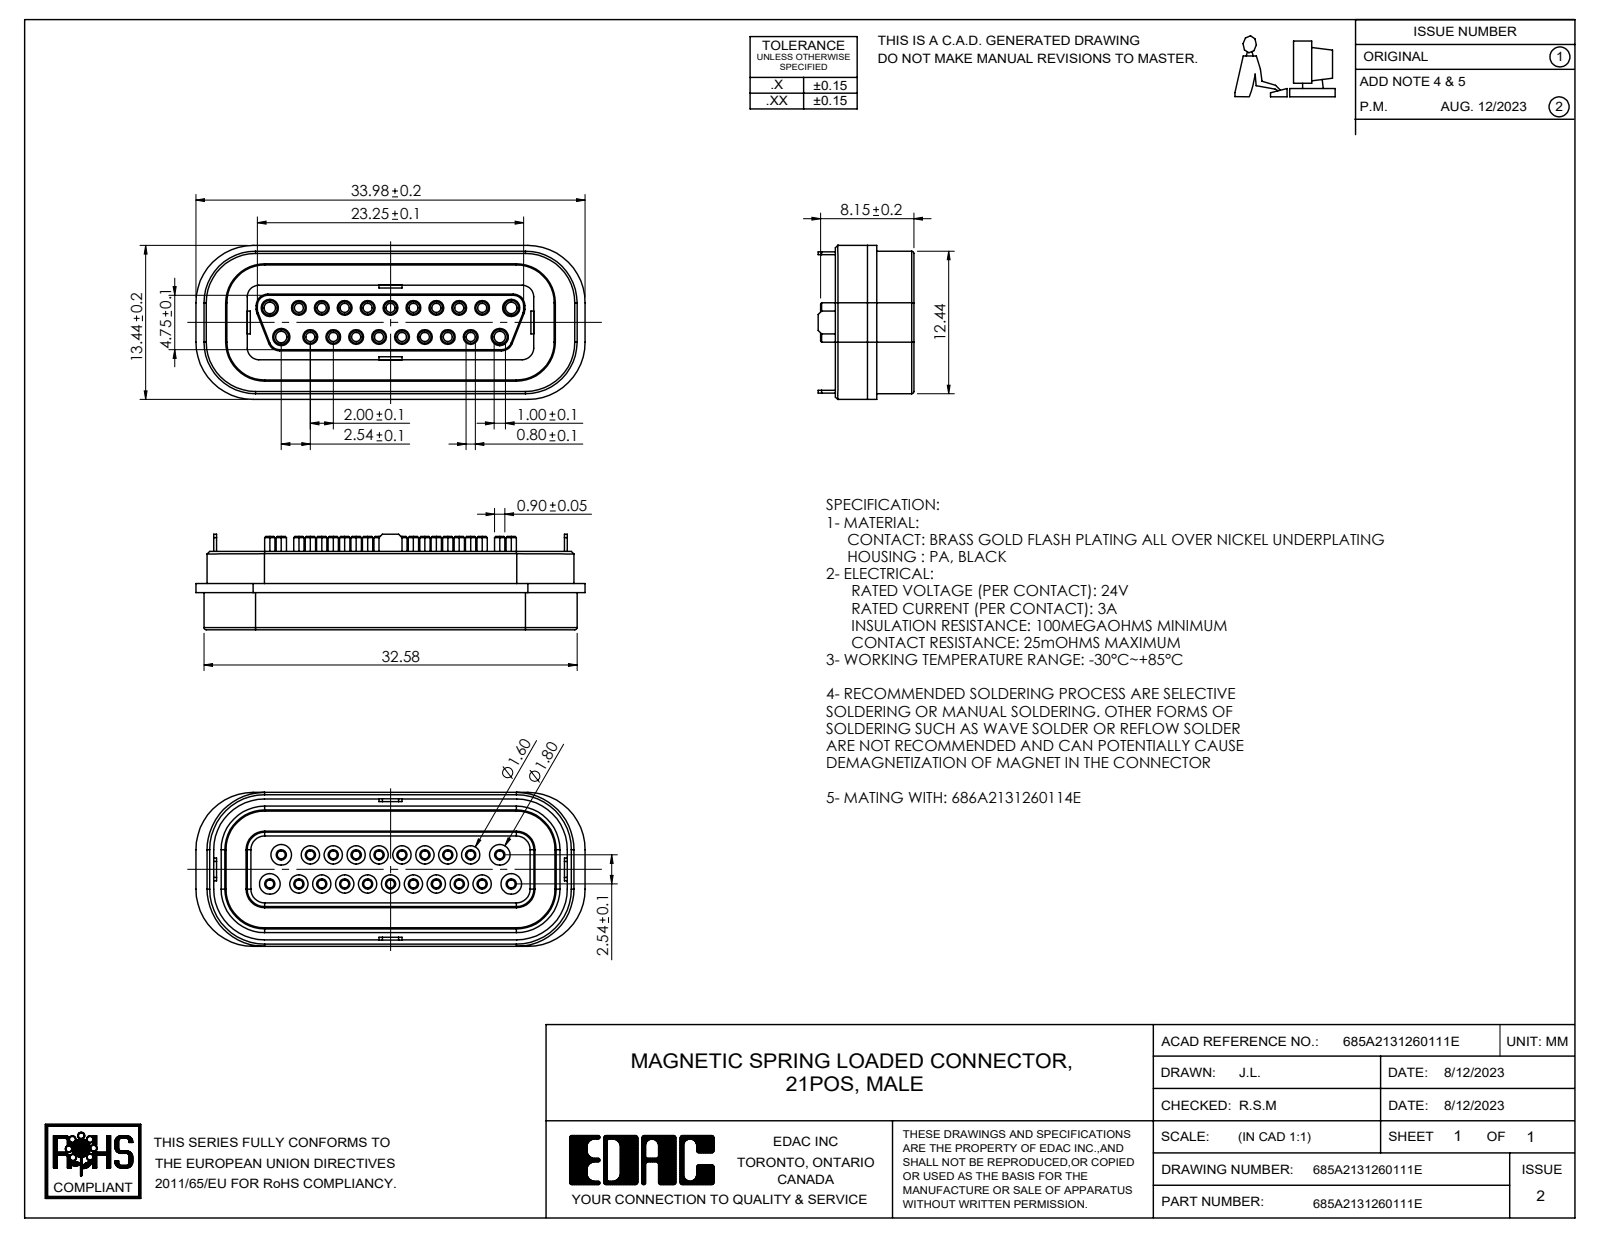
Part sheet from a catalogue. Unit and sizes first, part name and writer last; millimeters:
Units: millimetres
Overall size (bounding box): 33.98 × 13.44 × 8.35
Round holes (diameter × count): ⌀1.3 ×17, ⌀1.5 ×4
Round bosses / shafts (diameter × count): ⌀0.9 ×21, ⌀1.6 ×17, ⌀0.8 ×17, ⌀1.8 ×4, ⌀1 ×4
Partial cylindrical surfaces — rounded edges, fillets, slot ends (radius × count): R0.1 ×28, R0.9 ×12, R5 ×8, R0.2 ×4, R1 ×4, R1.5 ×4, R1.52 ×4, R3.3 ×4
Main face-to-face distances: 1.98, 8.44, 8.42, 2, 10.42, 0.6, 1.96, 6.25, 0.5, 1.5
Hole centre spacings: 2.73, 2, 3.93, 4, 5.61, 6, 7.45, 8
Volume: 3 983 mm³ · Surface area: 5 901 mm²
Bodies: 7 solids, 1308 faces (448 planar, 540 cylindrical, 320 other)
Part name (STEP PRODUCT): 685A2131260111E
STEP written by: SolidWorks 2020 (AUTOMOTIVE_DESIGN)
